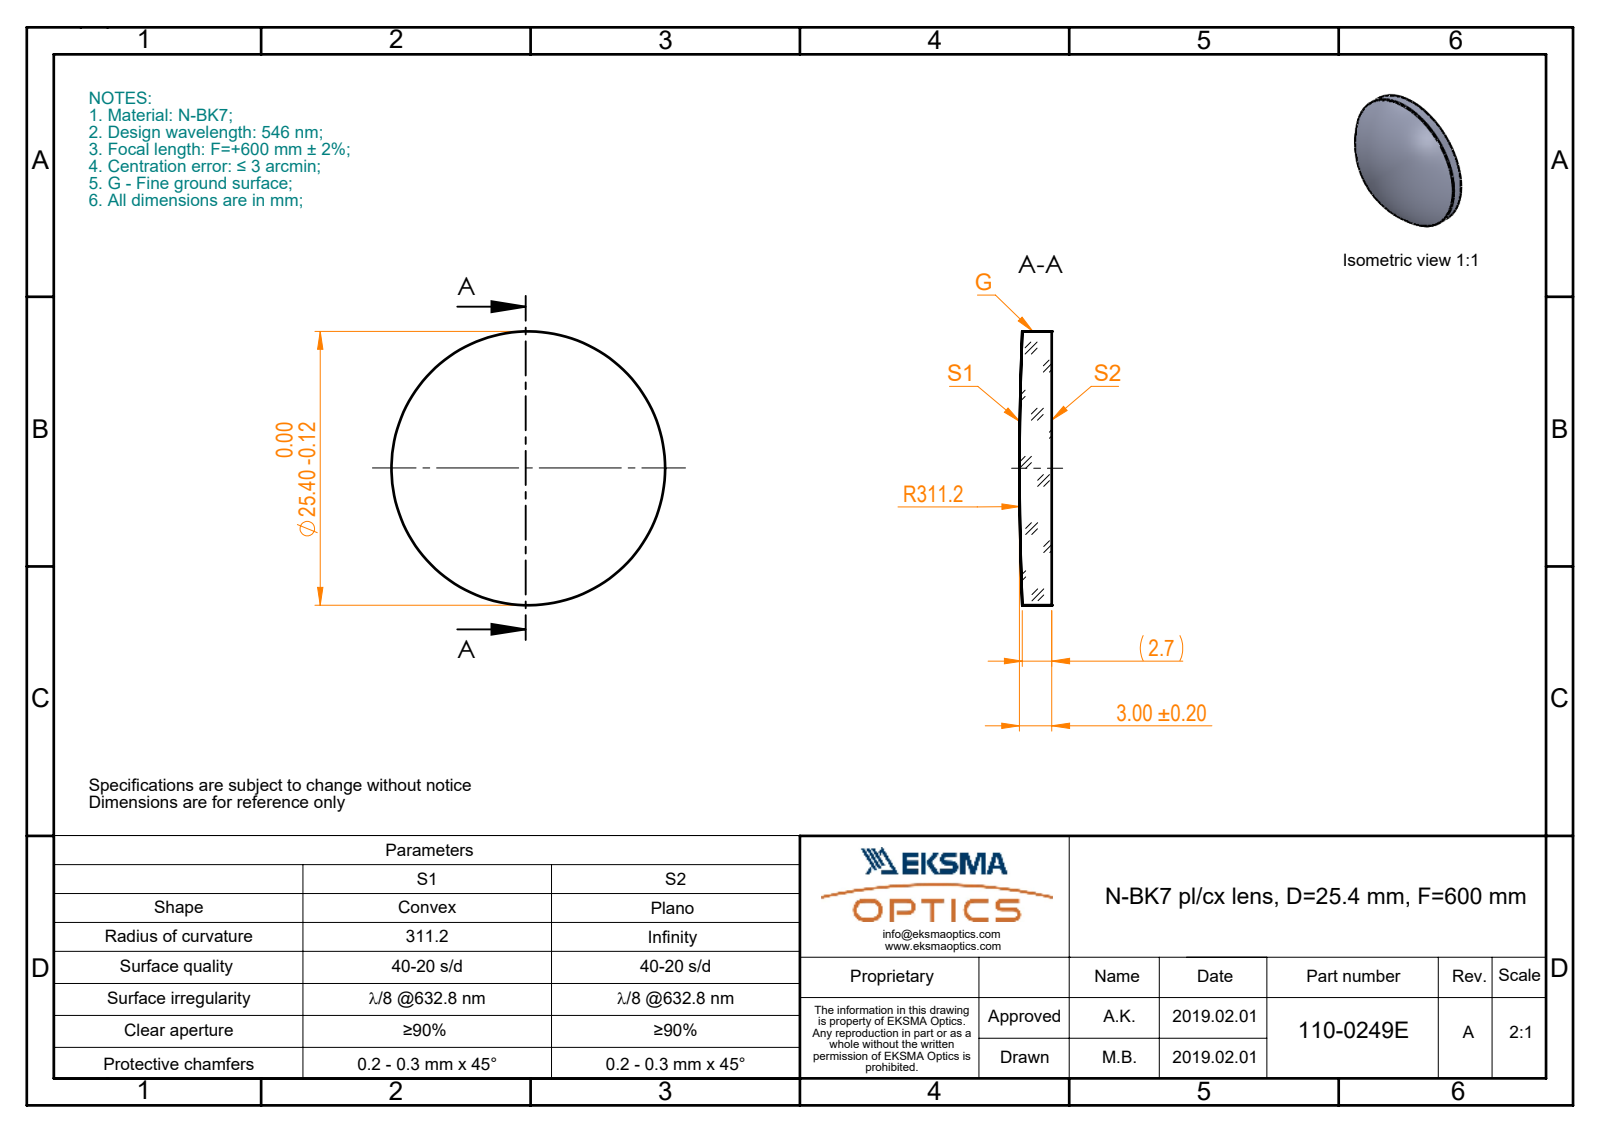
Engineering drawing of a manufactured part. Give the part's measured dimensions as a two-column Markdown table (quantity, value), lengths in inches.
| quantity | value |
| --- | --- |
| part name | 110-0249E BK7 pl-cx 25.4 F600 |
| STEP written by | SolidWorks 2017 (CONFIG_CONTROL_DESIGN) |
| units | inches |
| bodies | 1 solid, 5 faces (1 planar, 2 cylindrical, 2 other) |
| overall size | 1 × 1 × 0.118 |
| volume | 0.089 in³ |
| surface area | 1.91 in² |
| round bosses / shafts (diameter × count) | 1 × 1 |
